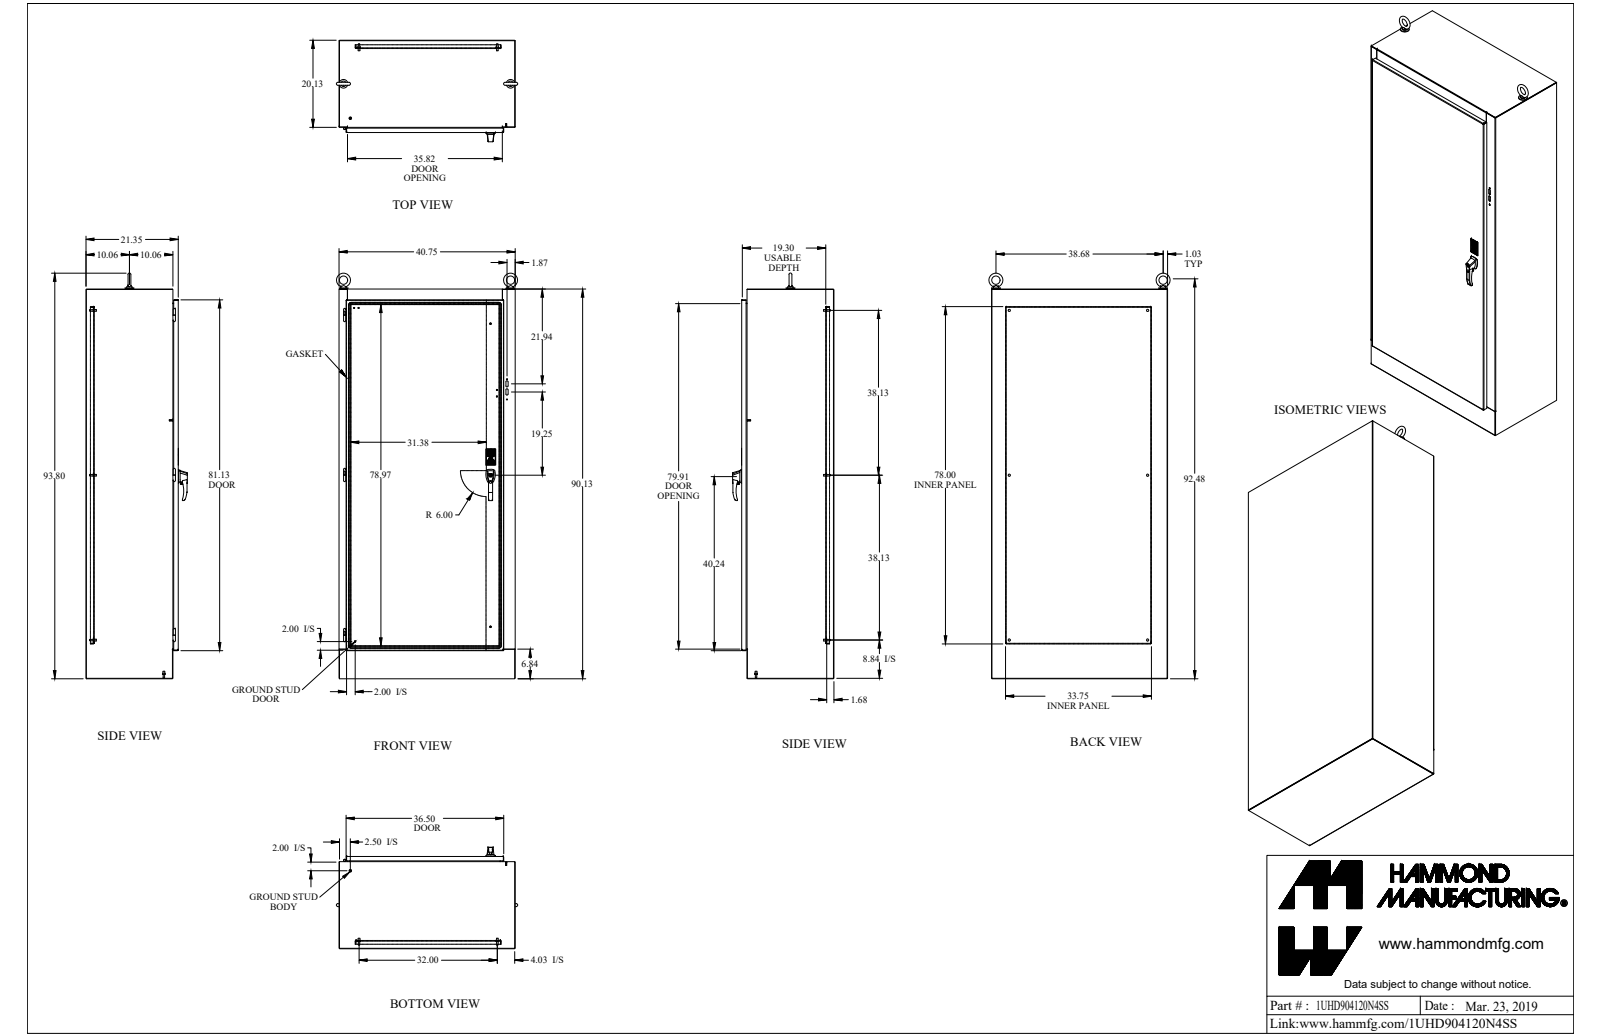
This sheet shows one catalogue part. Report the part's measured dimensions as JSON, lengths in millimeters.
{"part_name": "1UHD904120N4SS", "step_written_by": "SolidWorks 2018 (AUTOMOTIVE_DESIGN)", "units": "millimeters", "bodies": {"solids": 112, "faces": 2008, "planar": 1133, "cylindrical": 536, "other": 339}, "overall_size": [2382.5, 1065.1, 596], "volume_mm3": 29140000, "surface_area_mm2": 22890000, "round_holes": [[8.9, 7], [5, 6], [7.8, 6], [14.3, 6], [6.4, 5], [4, 4], [7.1, 4], [11.3, 4], [8, 3], [4.2, 2], [4.8, 2], [6.5, 2]], "round_bosses_or_shafts": [[6.4, 10], [25.4, 8], [9.5, 8], [16.5, 7], [8.4, 7], [4.8, 4], [15.9, 3], [12.7, 3]], "partial_cylinders_radius": [[3.2, 27], [1.2, 24], [3.6, 24], [12.7, 23], [1.5, 19], [6.4, 19], [0.4, 16], [0.8, 12]], "face_to_face_distances": [2.4, 539.9, 1032.6, 537.4, 542.3, 3.2, 48.4, 46, 491.4, 493.9], "hole_center_spacings": [812.8, 188.8, 189.7, 190.5, 327, 378.5, 773.7, 862]}
